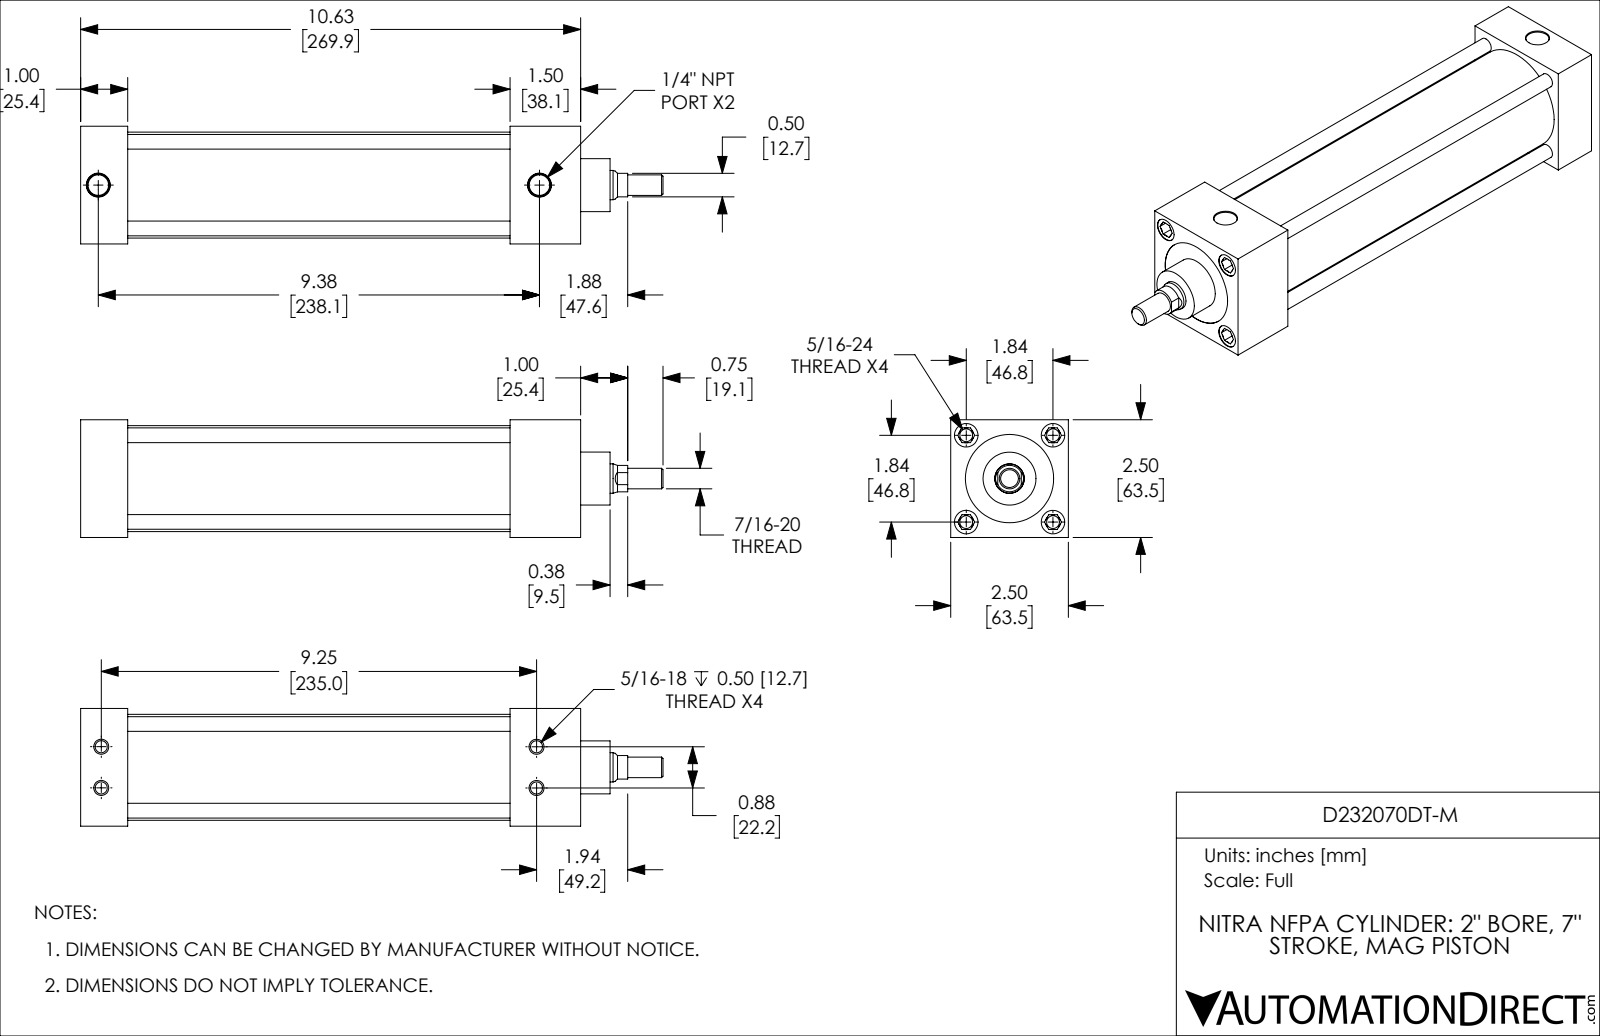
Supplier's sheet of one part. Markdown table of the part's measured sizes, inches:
| quantity | value |
| --- | --- |
| part name | D232070DT-M_BODY; D232070DT-M_PISTON_KK1; D232070DT-M |
| STEP written by | SolidWorks 2019 (CONFIG_CONTROL_DESIGN) |
| units | inches |
| bodies | 2 solids, 200 faces (58 planar, 62 cylindrical, 80 other) |
| overall size | 12.375 × 2.5 × 2.5 |
| volume | 30.58 in³ |
| surface area | 236.5 in² |
| round holes (diameter × count) | 0.272 × 7, 0.257 × 4, 0.5 × 4, 0.438 × 2, 0.626 × 1, 1.875 × 1, 2.001 × 1 |
| round bosses / shafts (diameter × count) | 0.312 × 4, 2.251 × 1, 1.999 × 1, 1.125 × 1, 0.624 × 1, 0.437 × 1 |
| partial cylindrical surfaces (radius × count) | 0.281 × 1 |
| main face-to-face distances | 2.5, 1, 9.125, 8.125, 1.125, 2.125, 7, 10.625, 9.625, 8.5 |
| hole center spacings | 1.84, 1.844, 1.301, 0.441, 0.443, 0.875, 1.304, 2.602 |
